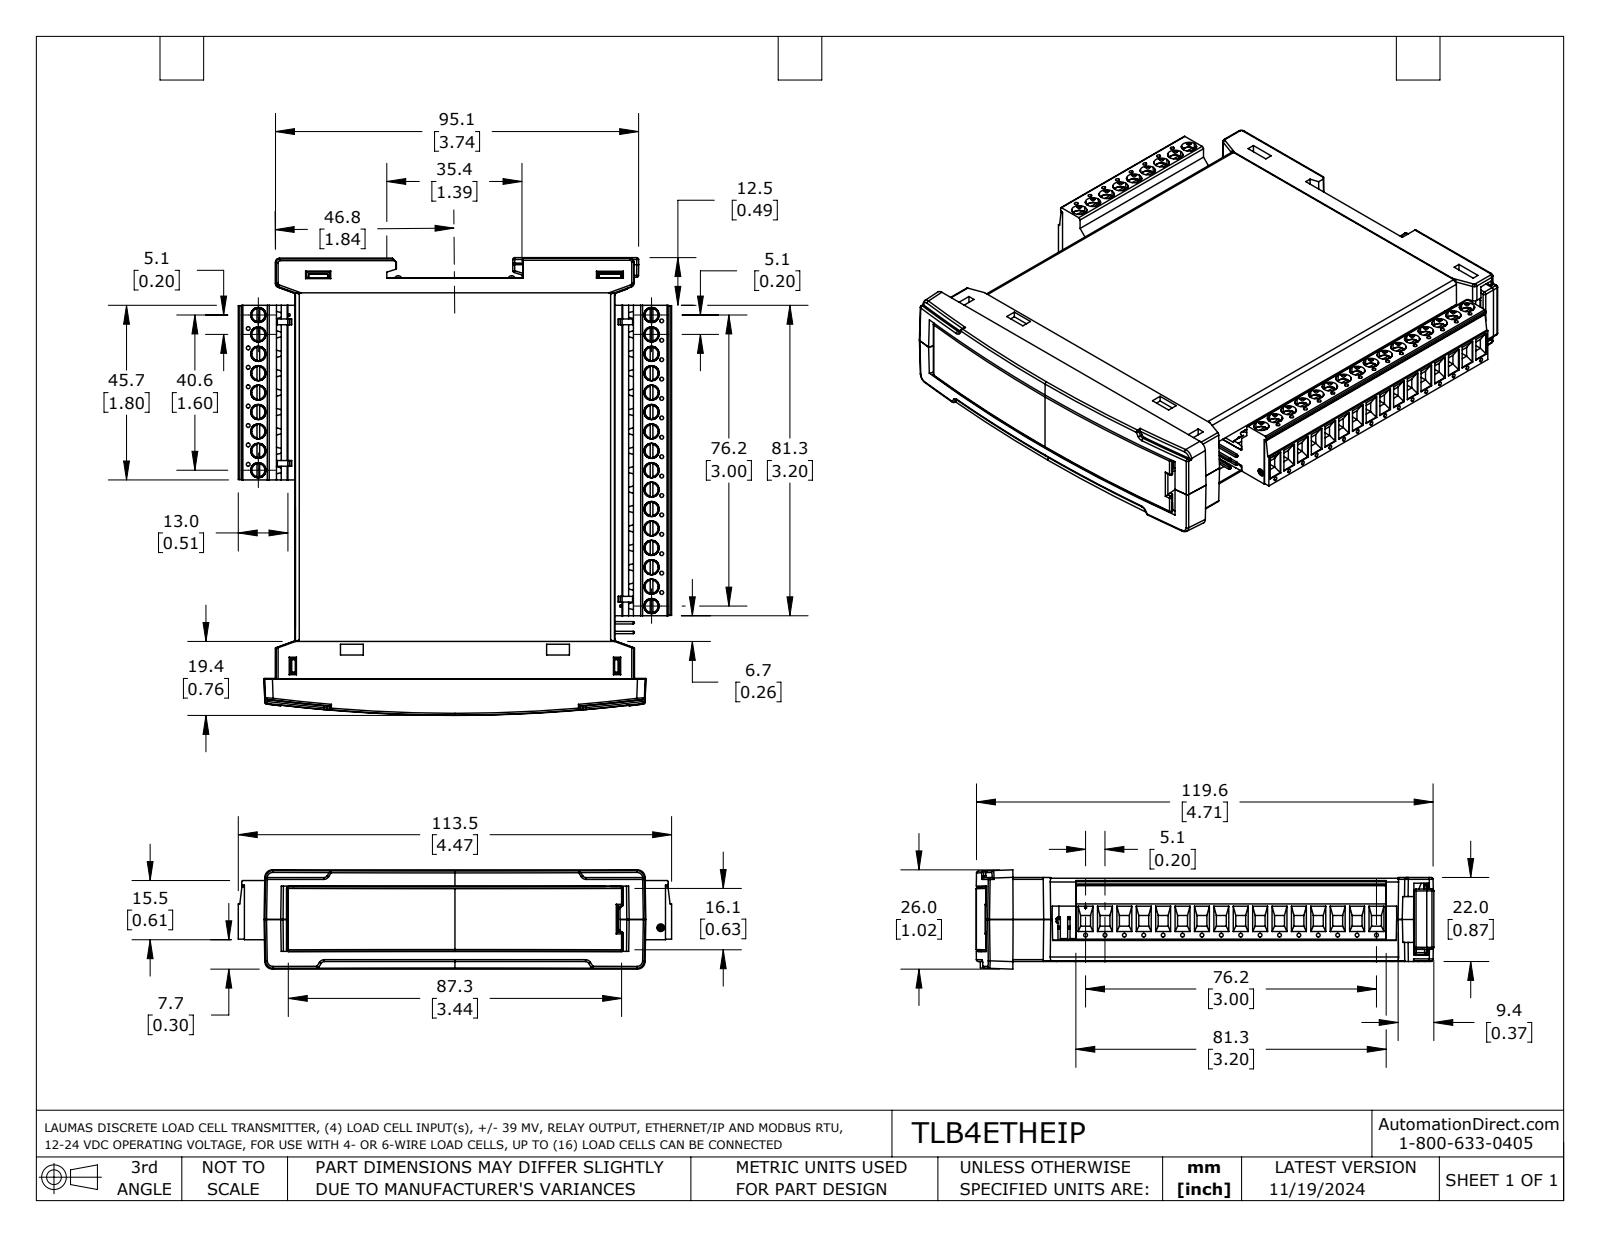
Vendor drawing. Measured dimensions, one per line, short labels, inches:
name: TLB4ETHEIP
written by: SolidWorks 2021 (AUTOMOTIVE_DESIGN)
unit: in
bodies: 16 solids, 6189 faces (3876 planar, 1679 cylindrical, 634 other)
size: 4.719 × 4.469 × 1.023
volume: 5.946 in³; area: 175.6 in²
holes: 55× ⌀0.039, 25× ⌀0.157, 16× ⌀0.059, 16× ⌀0.146, 6× ⌀0.079, 4× ⌀0.029, 4× ⌀0.035, 2× ⌀0.067
bosses: 25× ⌀0.152, 25× ⌀0.055, 16× ⌀0.108, 4× ⌀0.114, 2× ⌀0.06, 2× ⌀0.051, 1× ⌀0.093
rounds: 158× R0.02, 116× R0.004, 64× R0.005, 44× R0.012, 26× R0.039, 20× R0.008, 16× R0.069, 16× R0.118
face distances: 0.051, 0.799, 0.161, 0.098, 0.587, 0.059, 0.701, 0.748, 0.063, 0.65
hole spacings: 0.2, 0.4, 0.224, 0.6, 0.8, 0.22, 0.278, 0.413
